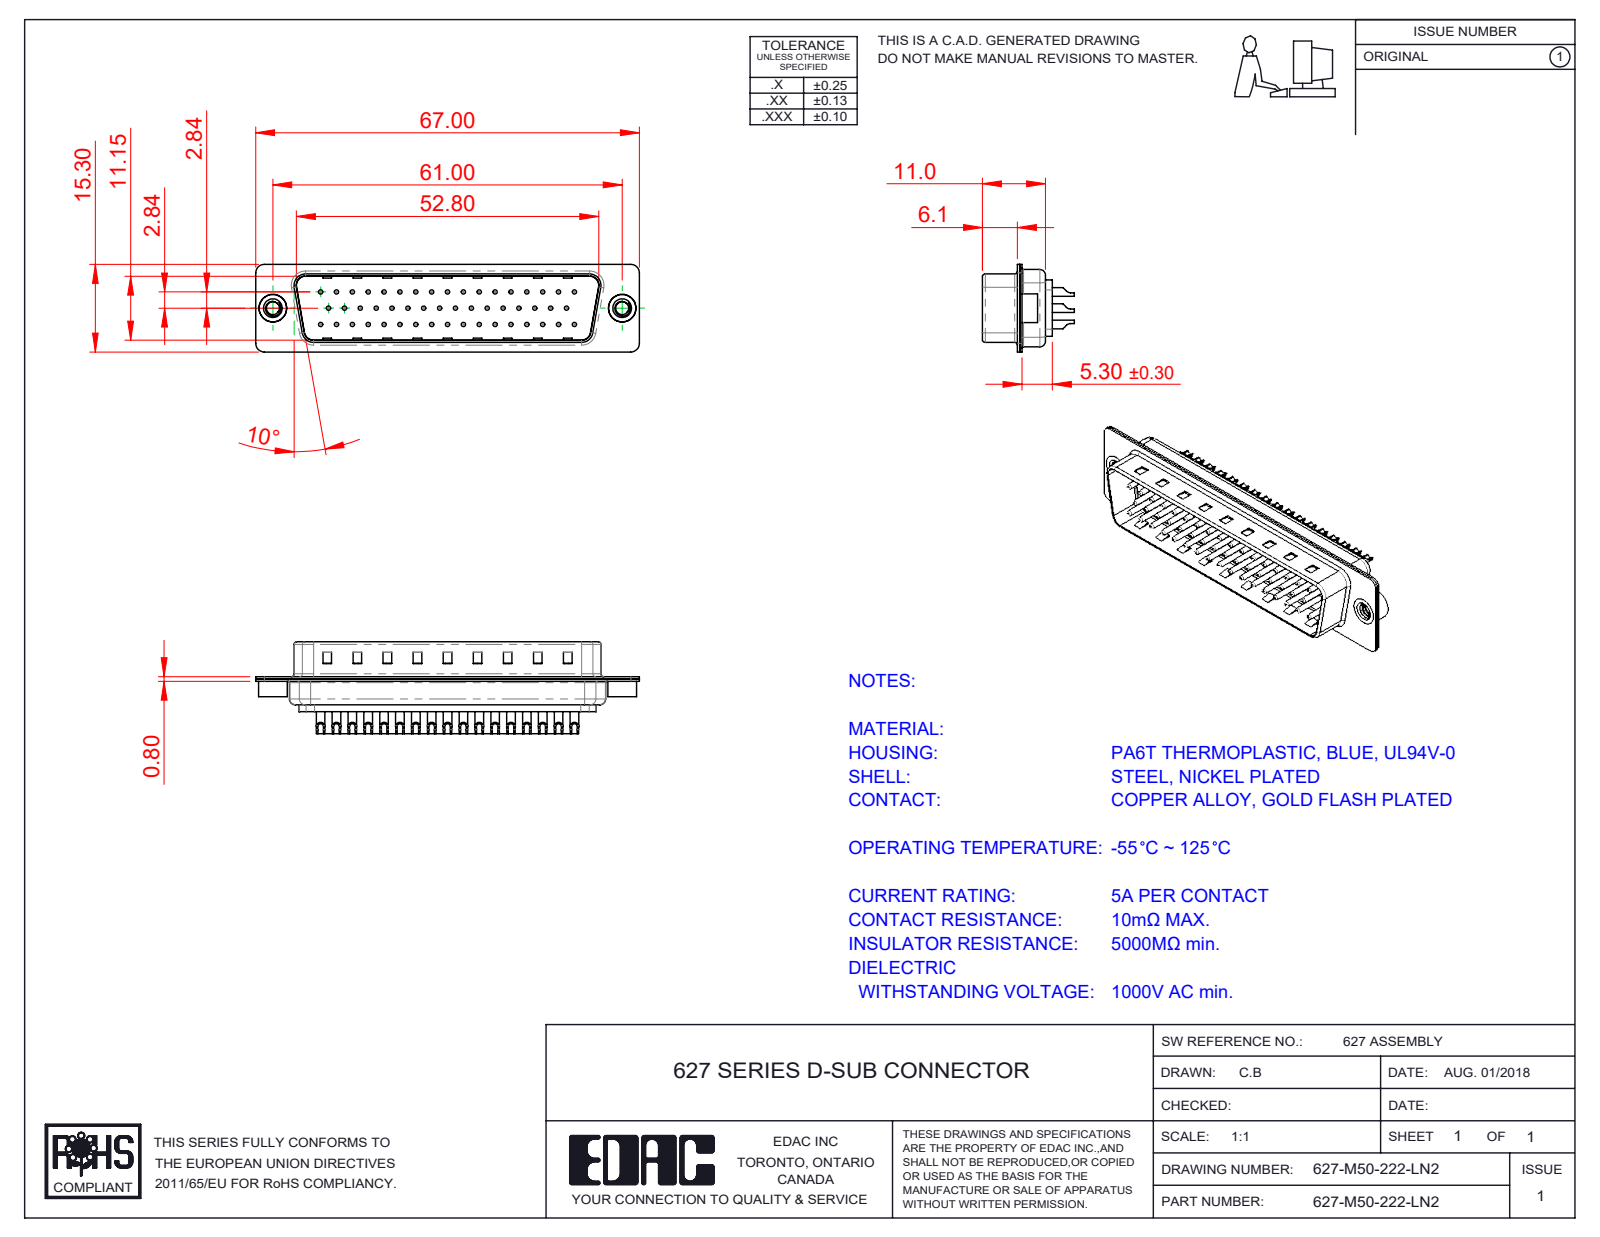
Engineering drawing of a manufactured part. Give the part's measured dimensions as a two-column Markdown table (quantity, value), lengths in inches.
| quantity | value |
| --- | --- |
| part name | 627M Housing_50 Contacts; 627-M50-222-LN2; 627M Contact Row 1_22; 627M Contact Row 2_22L (+4 more) |
| STEP written by | SolidWorks 2020 (CONFIG_CONTROL_DESIGN) |
| units | inches |
| bodies | 55 solids, 2262 faces (653 planar, 941 cylindrical, 668 other) |
| overall size | 2.638 × 0.632 × 0.602 |
| volume | 0.283 in³ |
| surface area | 17.31 in² |
| round holes (diameter × count) | 0.03 × 50, 0.039 × 50, 0.063 × 50, 0.079 × 50, 0.089 × 2, 0.157 × 2, 0.189 × 2 |
| round bosses / shafts (diameter × count) | 0.059 × 50, 0.197 × 2, 0.193 × 2 |
| partial cylindrical surfaces (radius × count) | 0.059 × 16, 0.079 × 12, 0.02 × 8, 0.063 × 8, 0.039 × 7, 0.01 × 4, 0.024 × 4, 0.026 × 4 |
| main face-to-face distances | 0.016, 0.455, 0.224, 0.24, 0.031, 0.03, 0.485, 0.485, 0.516, 0.209 |
| hole center spacings | 0.124, 0.109, 0.218, 0.327, 0.436, 0.545, 0.654, 0.198 |
